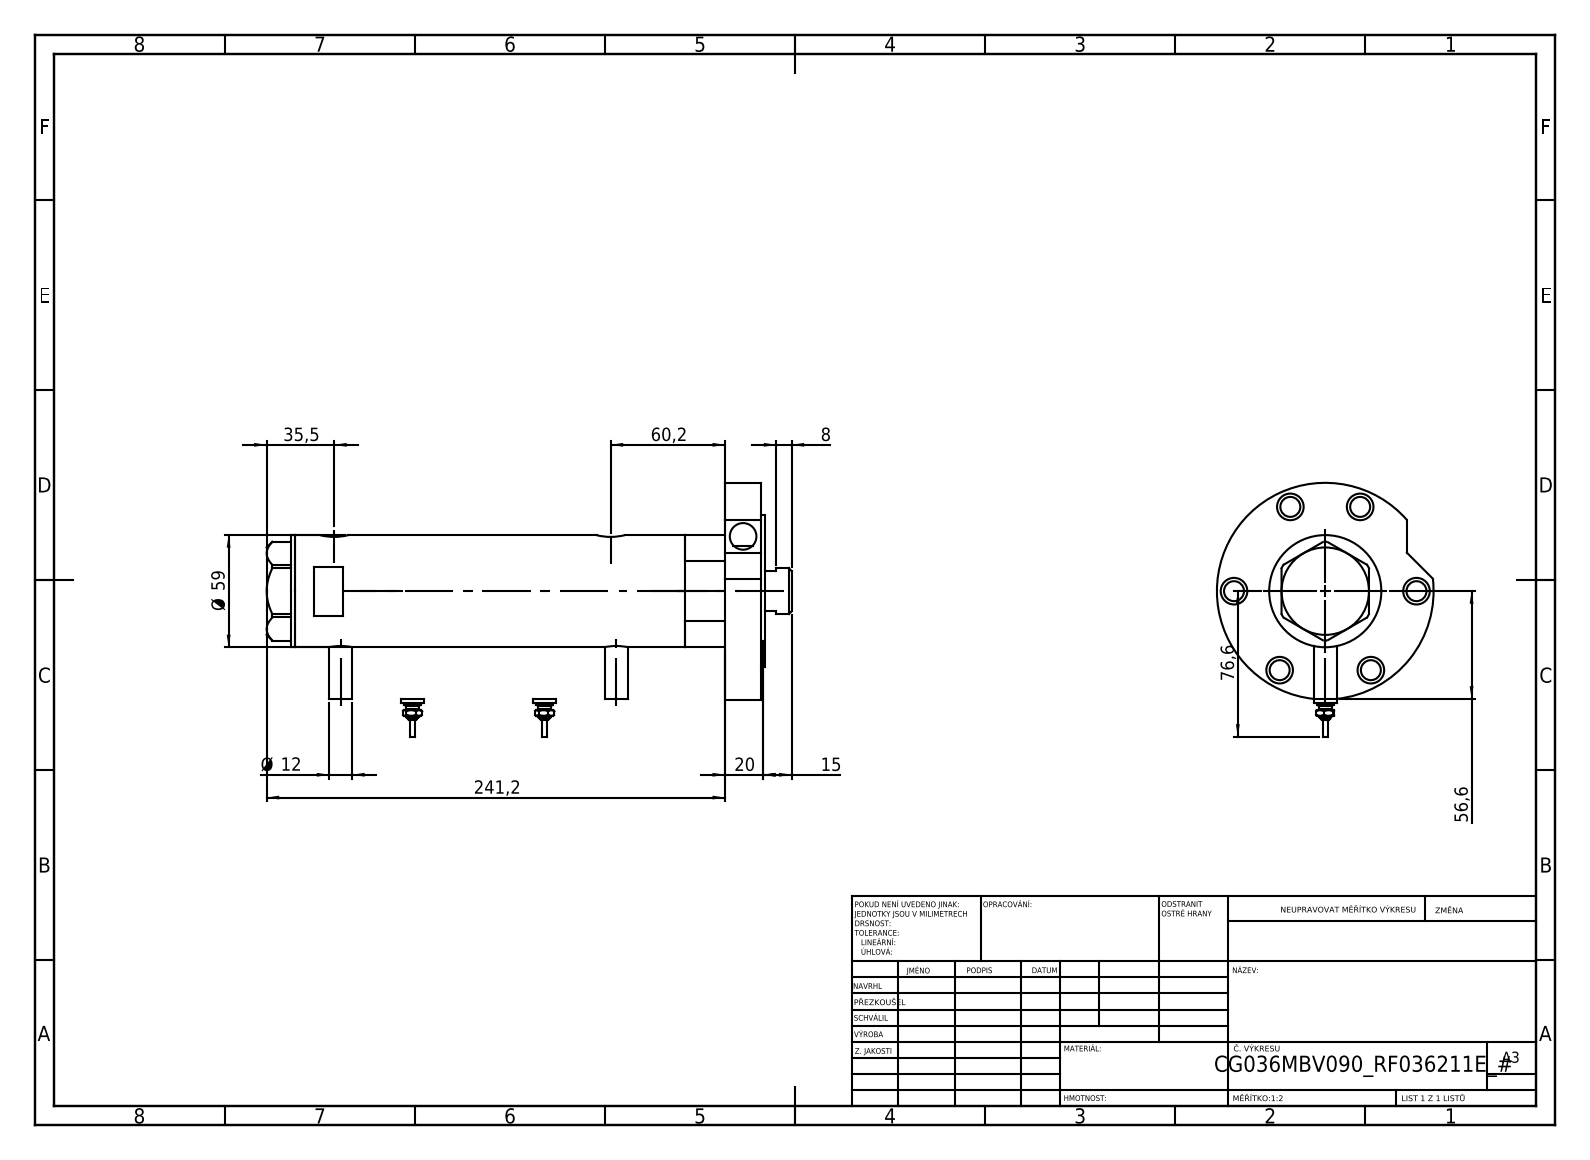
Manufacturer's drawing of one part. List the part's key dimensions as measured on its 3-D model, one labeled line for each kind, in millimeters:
Part name (STEP PRODUCT): V270CG_FRONT; V270CG_MIDDLE; V270CG_RF211E; V270CG_BACK (+2 more)
STEP written by: SolidWorks 2019 (CONFIG_CONTROL_DESIGN)
Units: millimetres
Bodies: 7 solids, 256 faces (90 planar, 102 cylindrical, 64 other)
Overall size (bounding box): 276.2 × 133.6 × 114
Volume: 777 268 mm³ · Surface area: 161 593 mm²
Round holes (diameter × count): ⌀14 ×7, ⌀10.5 ×6, ⌀9.73 ×2, ⌀12.5 ×2, ⌀15 ×2, ⌀8.5 ×1, ⌀25 ×1, ⌀26.5 ×1, ⌀36 ×1, ⌀40 ×1, ⌀48 ×1, ⌀52 ×1
Round bosses / shafts (diameter × count): ⌀12 ×4, ⌀9 ×2, ⌀7 ×2, ⌀4.5 ×2, ⌀2.5 ×2, ⌀114 ×1, ⌀80 ×1, ⌀59 ×1
Main face-to-face distances: 2, 19, 21, 247.2, 226.2, 245.2, 167.2, 59, 78, 80
Hole centre spacings: 48, 53.34, 79.82, 83.14, 86.1, 95.8, 2.9, 3.5
